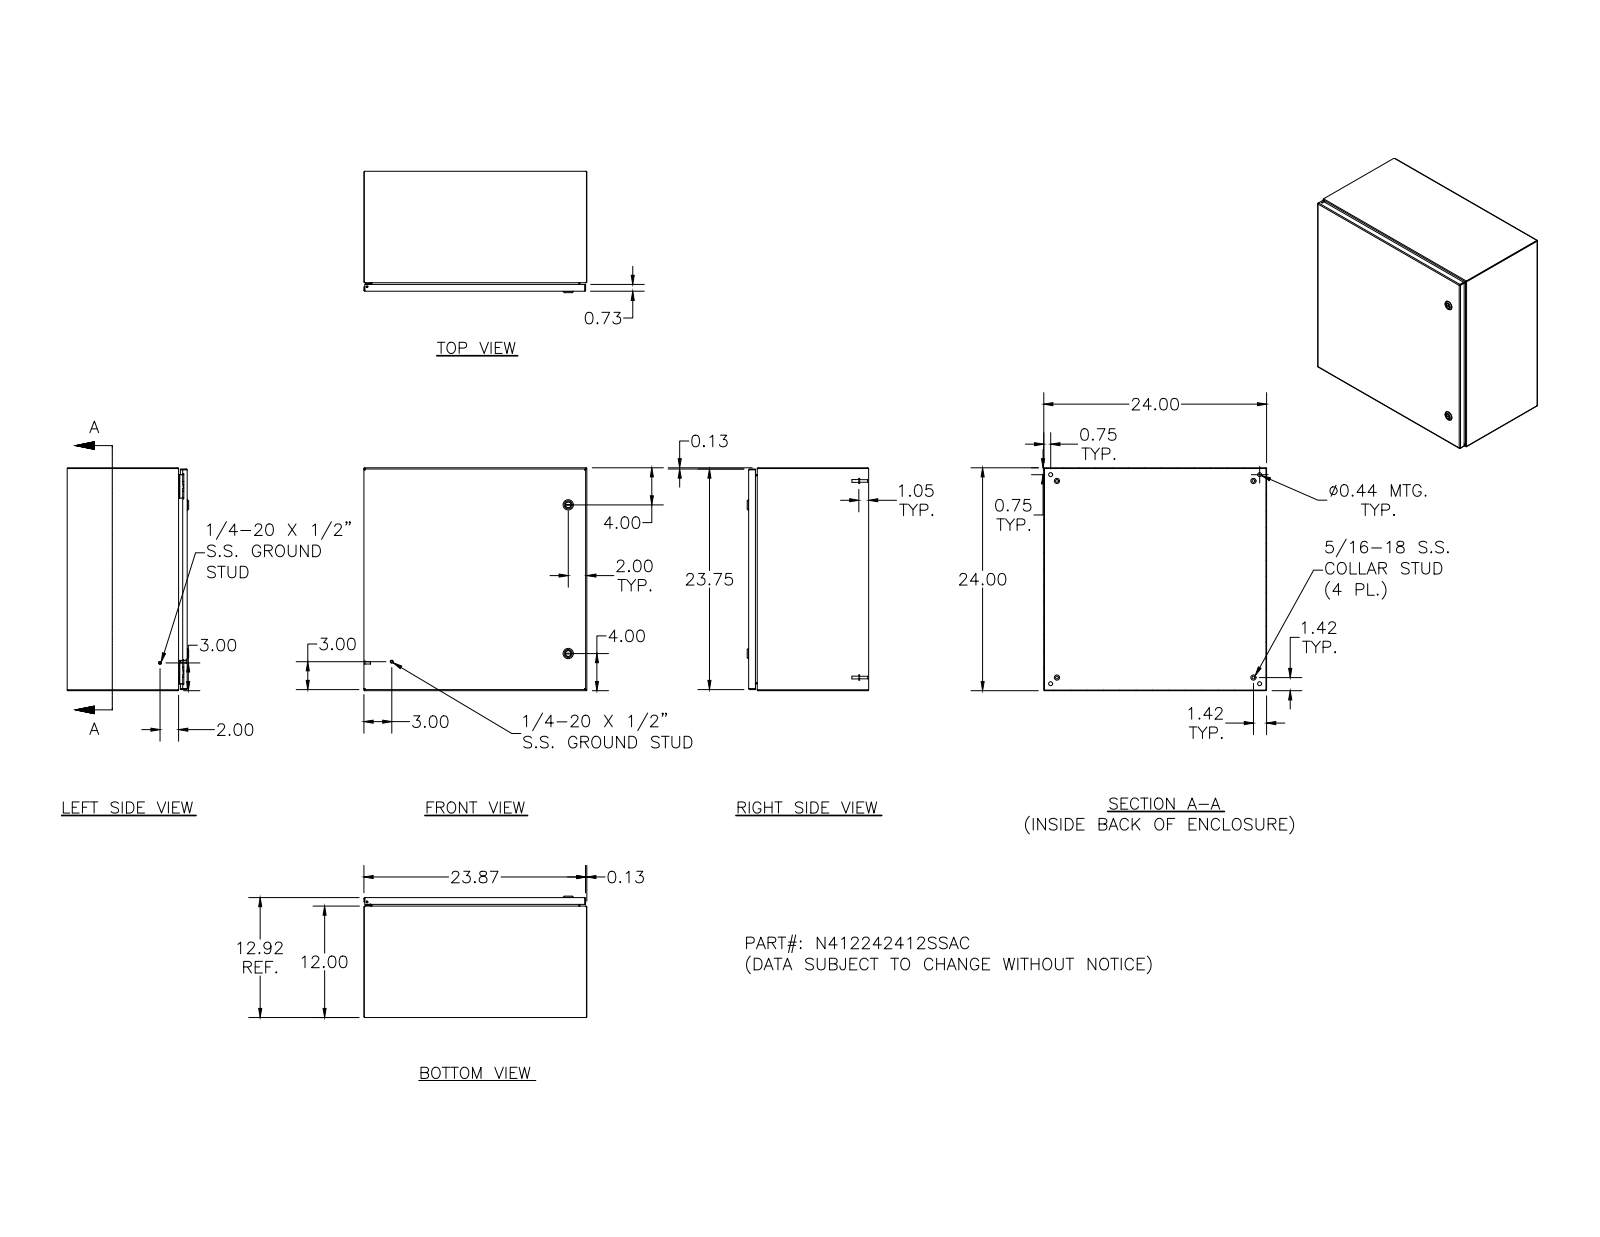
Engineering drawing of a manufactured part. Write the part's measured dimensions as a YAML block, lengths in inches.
part_name: "N412242412SSAC; N412242412SSACBKP; 388151; N4122424SSACLID (+8 more)"
step_written_by: "Autodesk Inventor 2011 (AUTOMOTIVE_DESIGN)"
units: inches
bodies: {solids: 42, faces: 1662, planar: 698, cylindrical: 588, other: 376}
overall_size: [24, 24, 13.075]
volume: 185.4
surface_area: 5029
round_holes:
  - {diameter: 0.188, count: 5}
  - {diameter: 0.093, count: 4}
  - {diameter: 0.152, count: 4}
  - {diameter: 0.167, count: 4}
  - {diameter: 0.172, count: 4}
  - {diameter: 0.437, count: 4}
  - {diameter: 0.156, count: 2}
  - {diameter: 0.197, count: 2}
  - {diameter: 0.315, count: 2}
  - {diameter: 0.394, count: 2}
  - {diameter: 0.402, count: 2}
  - {diameter: 0.634, count: 2}
round_bosses_or_shafts:
  - {diameter: 0.25, count: 10}
  - {diameter: 0.563, count: 4}
  - {diameter: 0.36, count: 4}
  - {diameter: 0.32, count: 4}
  - {diameter: 0.3, count: 4}
  - {diameter: 0.275, count: 4}
  - {diameter: 0.256, count: 4}
  - {diameter: 0.164, count: 4}
partial_cylinders:
  - {radius: 0.05, count: 26}
  - {radius: 0.016, count: 18}
  - {radius: 0.016, count: 16}
  - {radius: 0.09, count: 16}
  - {radius: 0.02, count: 15}
  - {radius: 0.031, count: 14}
  - {radius: 0.125, count: 14}
  - {radius: 0.032, count: 8}
face_to_face_distances: [0.074, 23.926, 12.843, 24, 23.852, 12.917, 12.769, 11.926, 0.917, 0.739]
hole_center_spacings: [20, 0.017, 0.66, 22.5, 22.869, 0.019, 0.5, 0.648]
